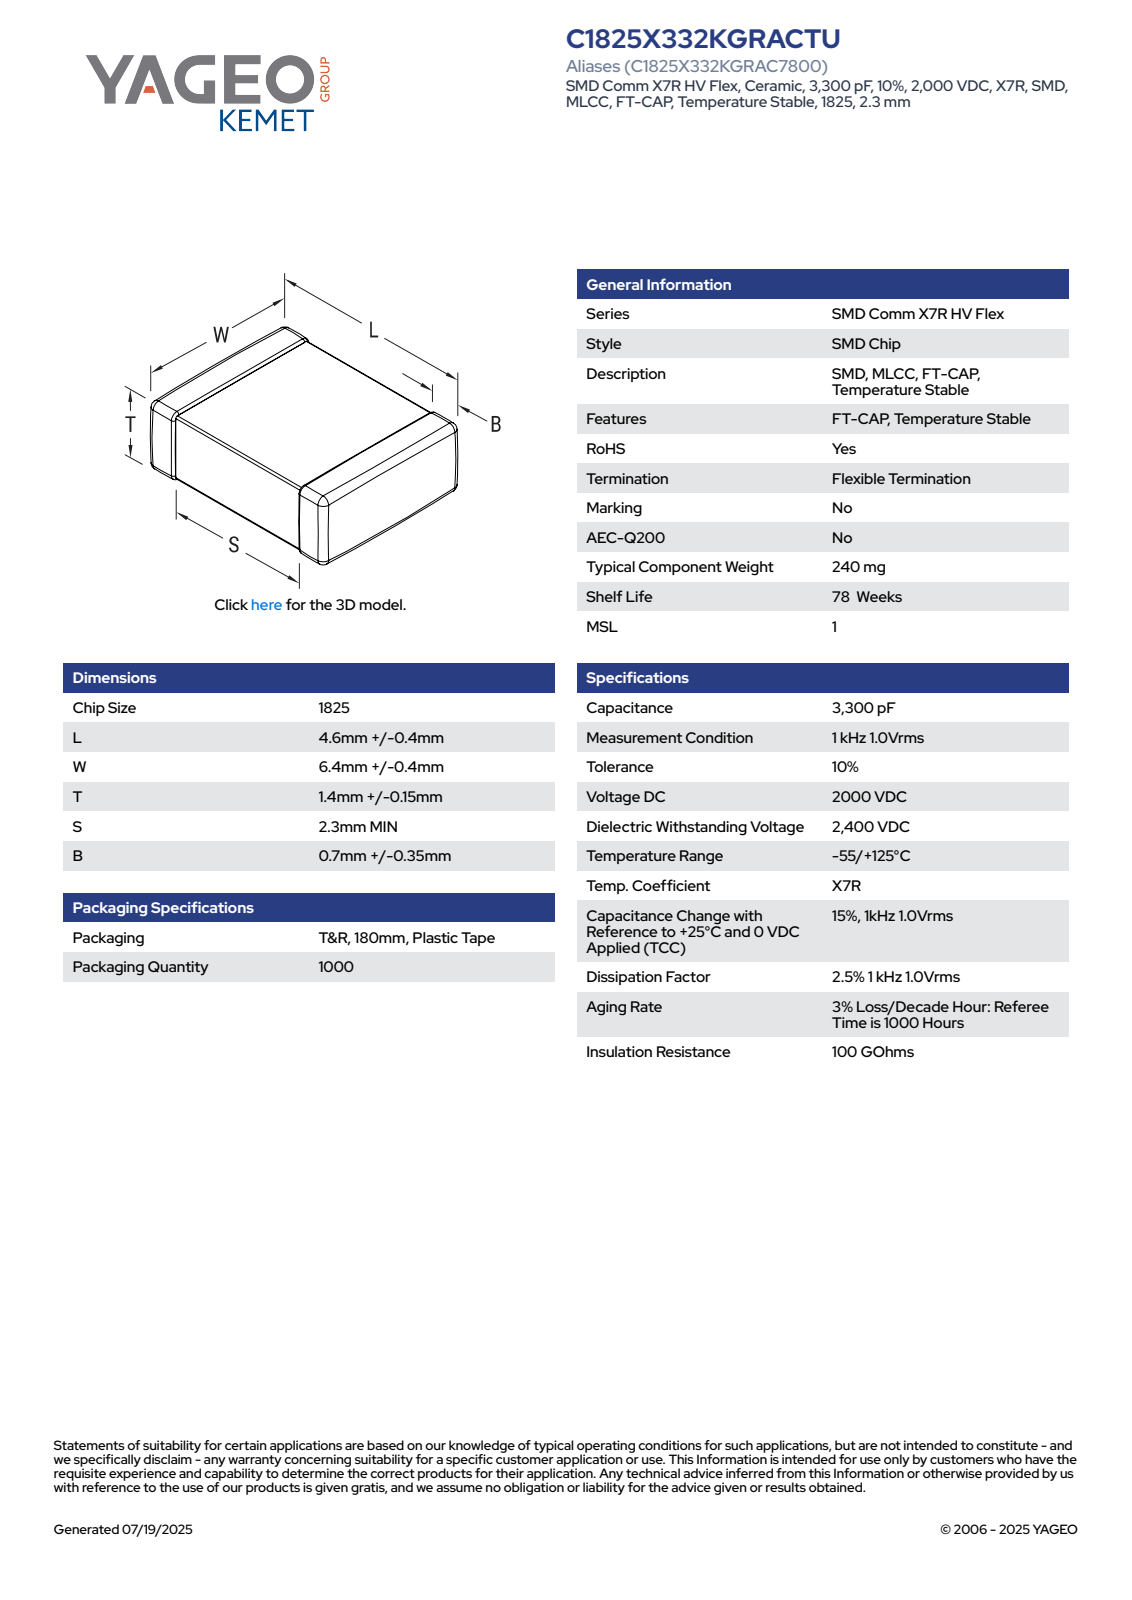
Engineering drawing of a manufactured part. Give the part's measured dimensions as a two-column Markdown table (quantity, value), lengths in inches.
| quantity | value |
| --- | --- |
| part name | CCS_CCSTD_1825_L5W6.8T1.55B0.7 |
| STEP written by | SolidWorks 2021 (AUTOMOTIVE_DESIGN) |
| units | inches |
| bodies | 4 solids, 125 faces (71 planar, 38 cylindrical, 16 other) |
| overall size | 0.268 × 0.197 × 0.061 |
| volume | 0.003 in³ |
| surface area | 0.166 in² |
| partial cylindrical surfaces (radius × count) | 0.006 × 24 |
| main face-to-face distances | 0.056, 0.05, 0.061, 0.197, 0.262, 0.257, 0.268, 0.039, 0.091, 0.067 |
